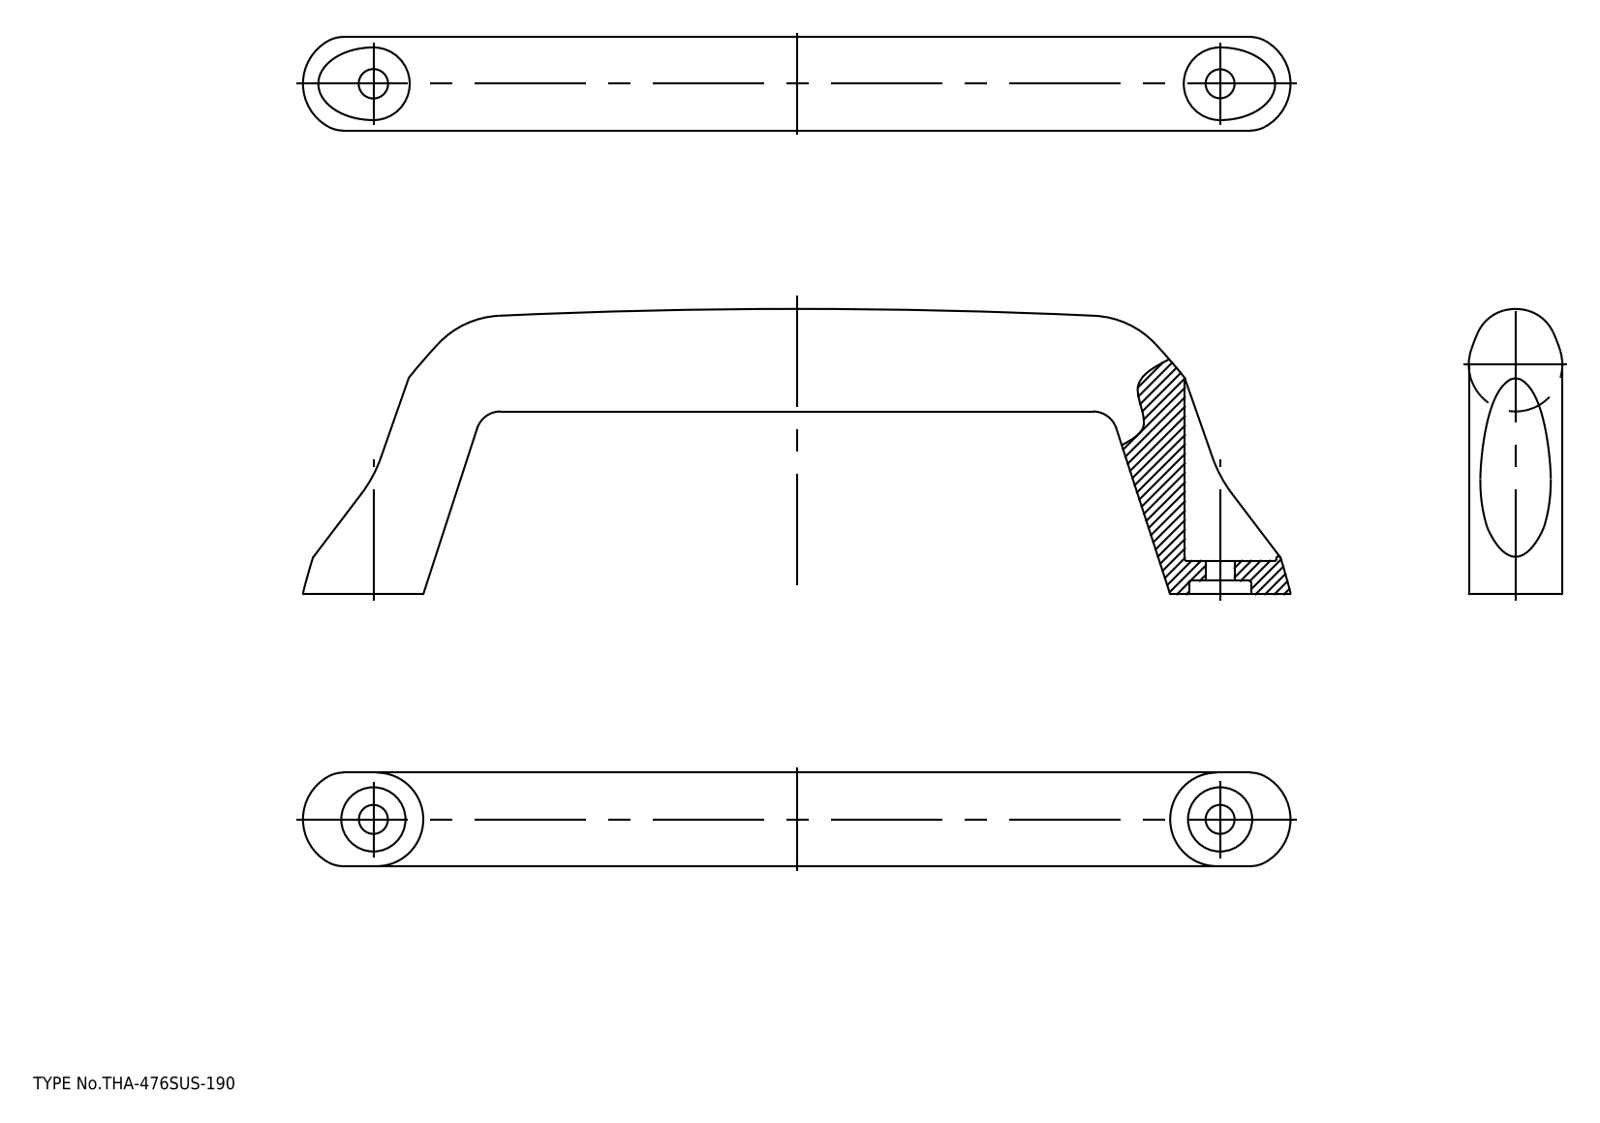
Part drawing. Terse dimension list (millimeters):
written by: spGate 20.6.3 (****-****-****-****) (AUTOMOTIVE_DESIGN)
unit: mm
bodies: 1 solid, 48 faces (6 planar, 10 cylindrical, 32 other)
size: 221.49 × 64 × 21.36
volume: 84 619 mm³; area: 20 640 mm²
holes: 2× ⌀6.5, 2× ⌀14.4
rounds: 2× R8.15
face distances: 7.5, 3, 4.5
hole spacings: 190
